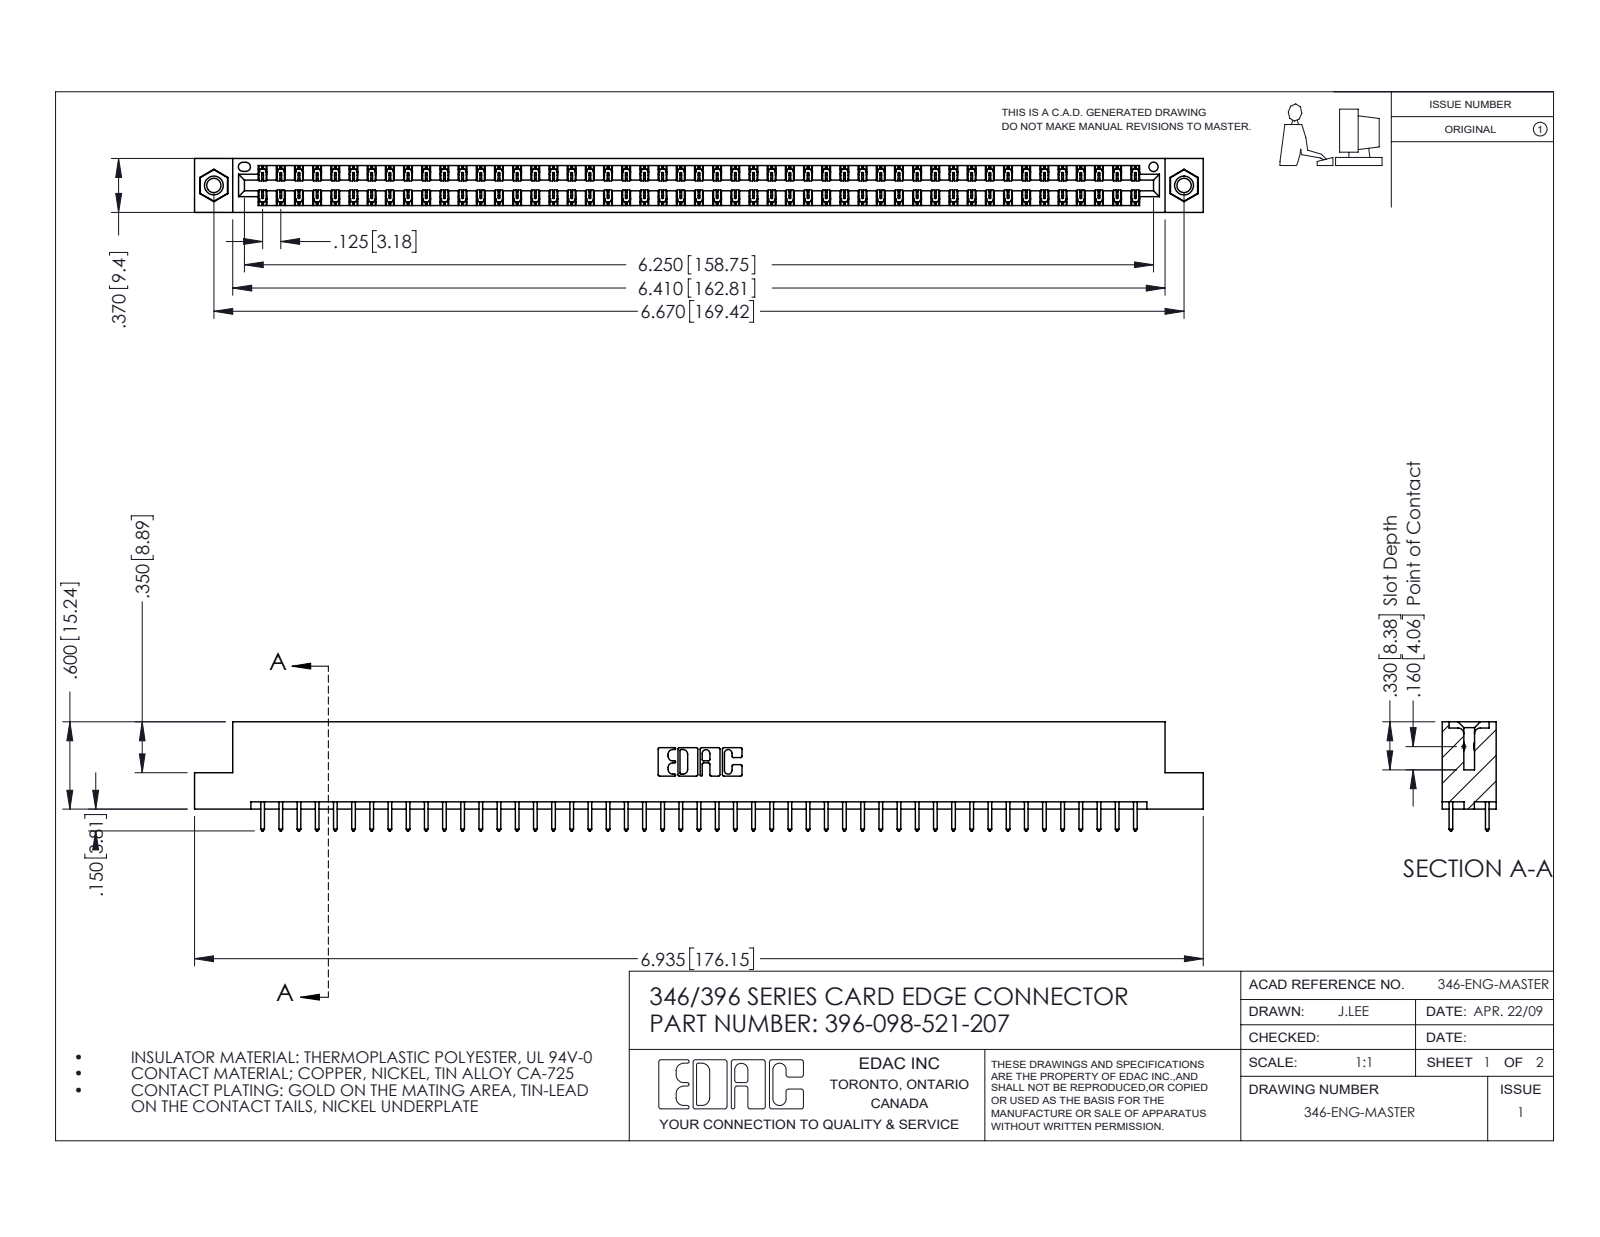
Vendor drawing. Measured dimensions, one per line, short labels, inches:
name: 396-098-521-207; 345-250-001_345-250-005-103; 346 Part_Flush Mounting Lugs - 0.156 Dia-TI; 345-292-001_345-293-121
written by: SolidWorks 2016 (CONFIG_CONTROL_DESIGN)
unit: in
bodies: 101 solids, 5278 faces (3538 planar, 1724 cylindrical, 16 other)
size: 6.935 × 0.75 × 0.37
volume: 1.048 in³; area: 36.4 in²
holes: 2× ⌀0.098, 2× ⌀0.125, 2× ⌀0.156, 1× ⌀0.064
bosses: 2× ⌀0.155
rounds: 147× R0.006, 98× R0.01, 22× R0.01, 6× R0.007, 6× R0.031, 3× R0.026, 2× R0.014, 2× R0.022
face distances: 0.048, 0.322, 0.37, 0.25, 0.072, 0.298, 0.025, 0.275, 0.148, 0.222
hole spacings: 0.246, 6.461, 6.67
